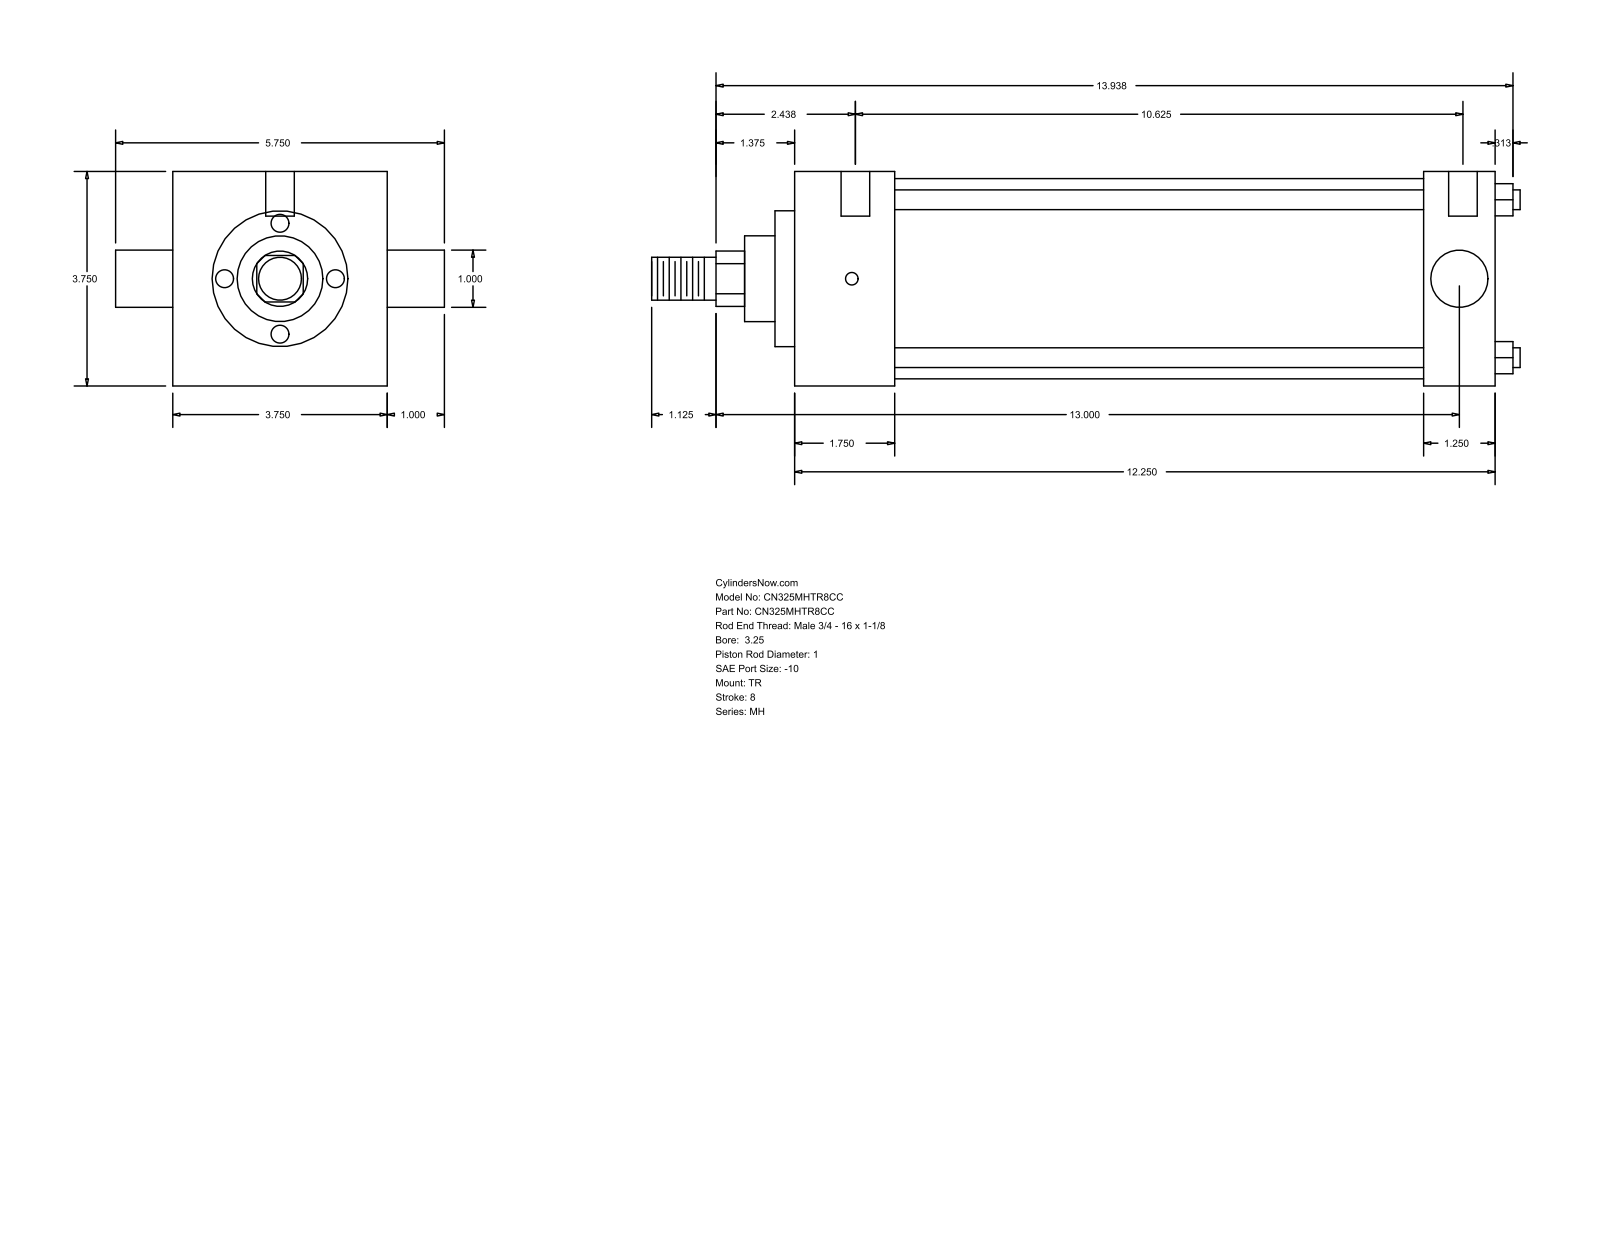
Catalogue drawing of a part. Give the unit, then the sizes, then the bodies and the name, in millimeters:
Units: millimetres
Overall size (bounding box): 385.76 × 146.05 × 95.25
Round holes (diameter × count): ⌀5.56 ×3, ⌀12.7 ×2
Round bosses / shafts (diameter × count): ⌀8.76 ×4, ⌀25.4 ×2, ⌀88.9 ×1, ⌀60.33 ×1, ⌀38.1 ×1, ⌀19.05 ×1
Partial cylindrical surfaces — rounded edges, fillets, slot ends (radius × count): R12.29 ×1
Main face-to-face distances: 95.24, 311.15, 44.46, 279.4, 234.94, 266.69, 31.75, 8.73, 53.19, 288.13
Hole centre spacings: 1.58, 4.76, 269.88, 271.46, 274.64, 276.22
Bodies: 0 solids, 86 faces (61 planar, 25 cylindrical, 0 other)
Part name (STEP PRODUCT): MH_TR__0325_1
STEP written by: GSSL Pune (CONFIG_CONTROL_DESIGN)
